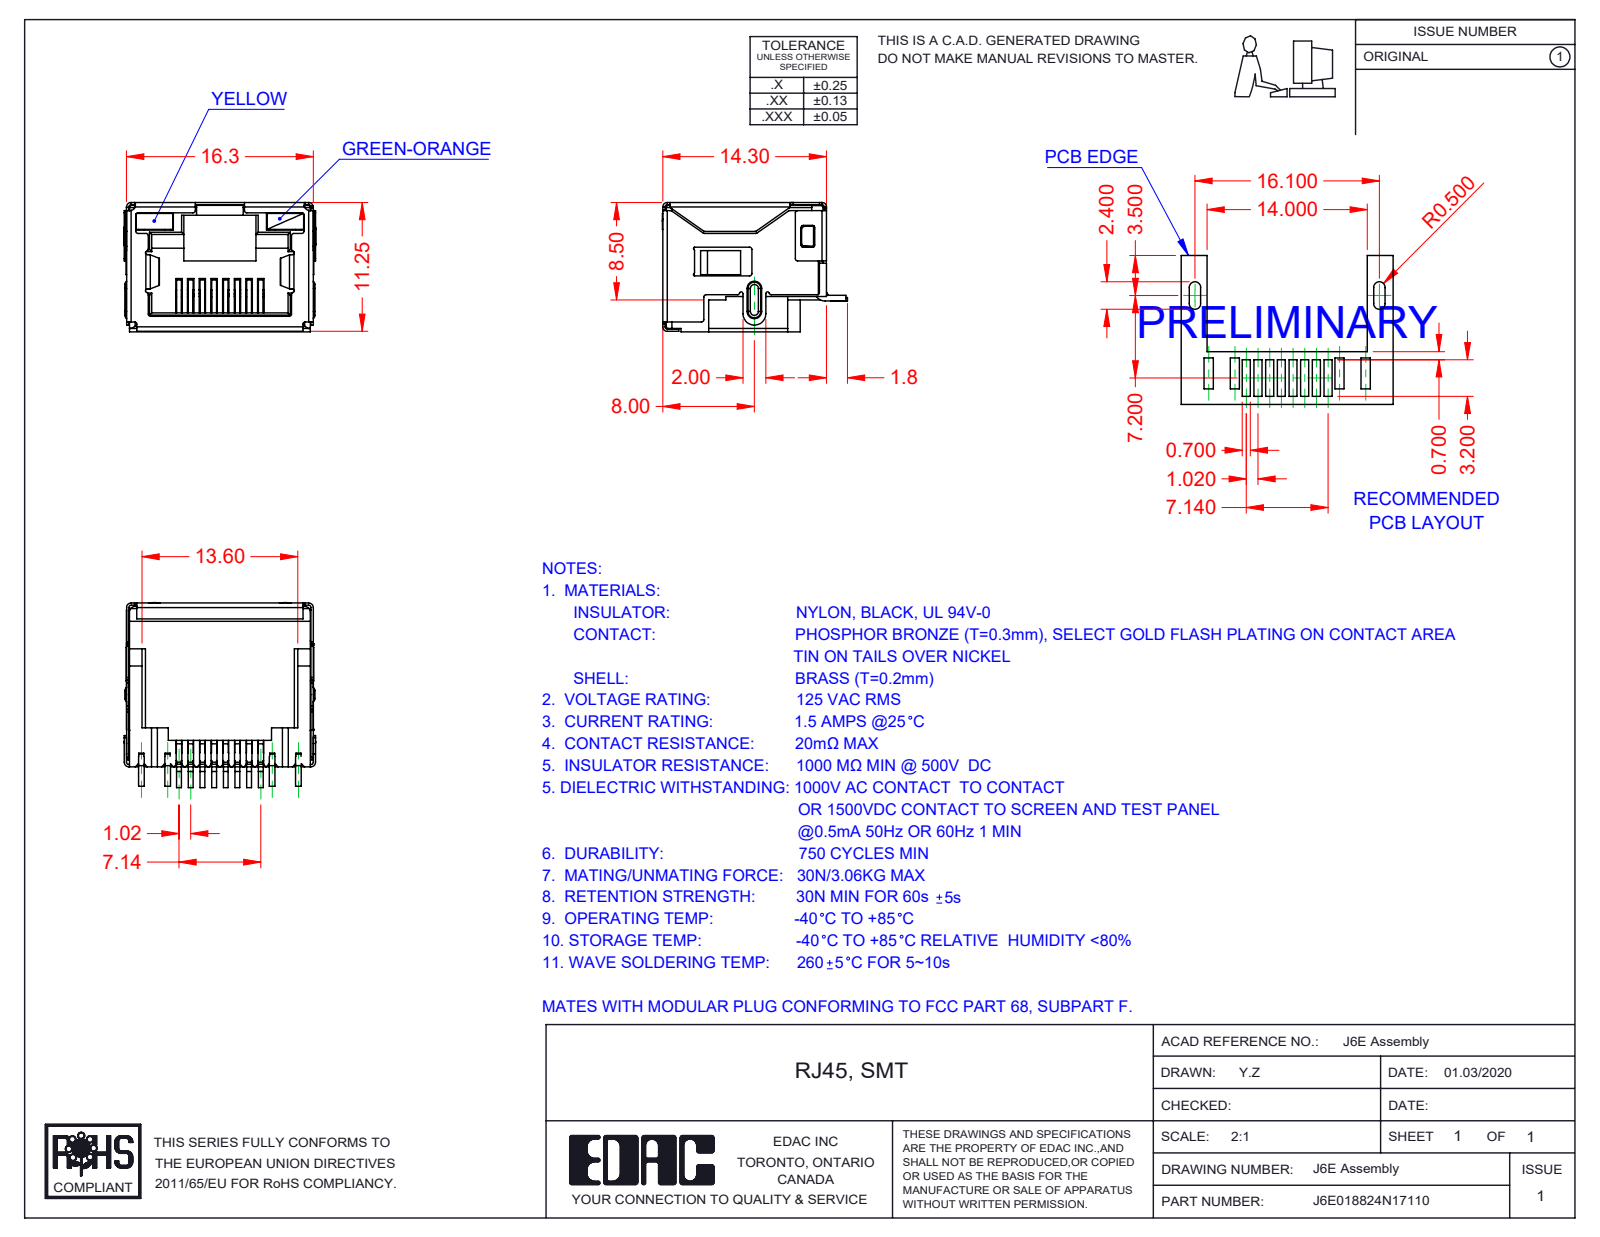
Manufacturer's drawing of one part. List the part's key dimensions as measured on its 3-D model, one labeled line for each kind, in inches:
Part name (STEP PRODUCT): 6E LED LH_1-Yellow; 6E Insulator_LED; J6E018824N17110; 6E LED RH_7-Green-Orange (+2 more)
STEP written by: SolidWorks 2016 (CONFIG_CONTROL_DESIGN)
Units: inches
Bodies: 12 solids, 1498 faces (1099 planar, 349 cylindrical, 50 other)
Overall size (bounding box): 0.659 × 0.636 × 0.445
Volume: 0.068 in³ · Surface area: 6.27 in²
Partial cylindrical surfaces — rounded edges, fillets, slot ends (radius × count): R0.008 ×82, R0.01 ×17, R0.016 ×13, R0.02 ×13, R0.004 ×10, R0.006 ×7, R0.012 ×4, R0.039 ×3
Main face-to-face distances: 0.435, 0.632, 0.634, 0.624, 0.437, 0.445, 0.094, 0.028, 0.388, 0.019
